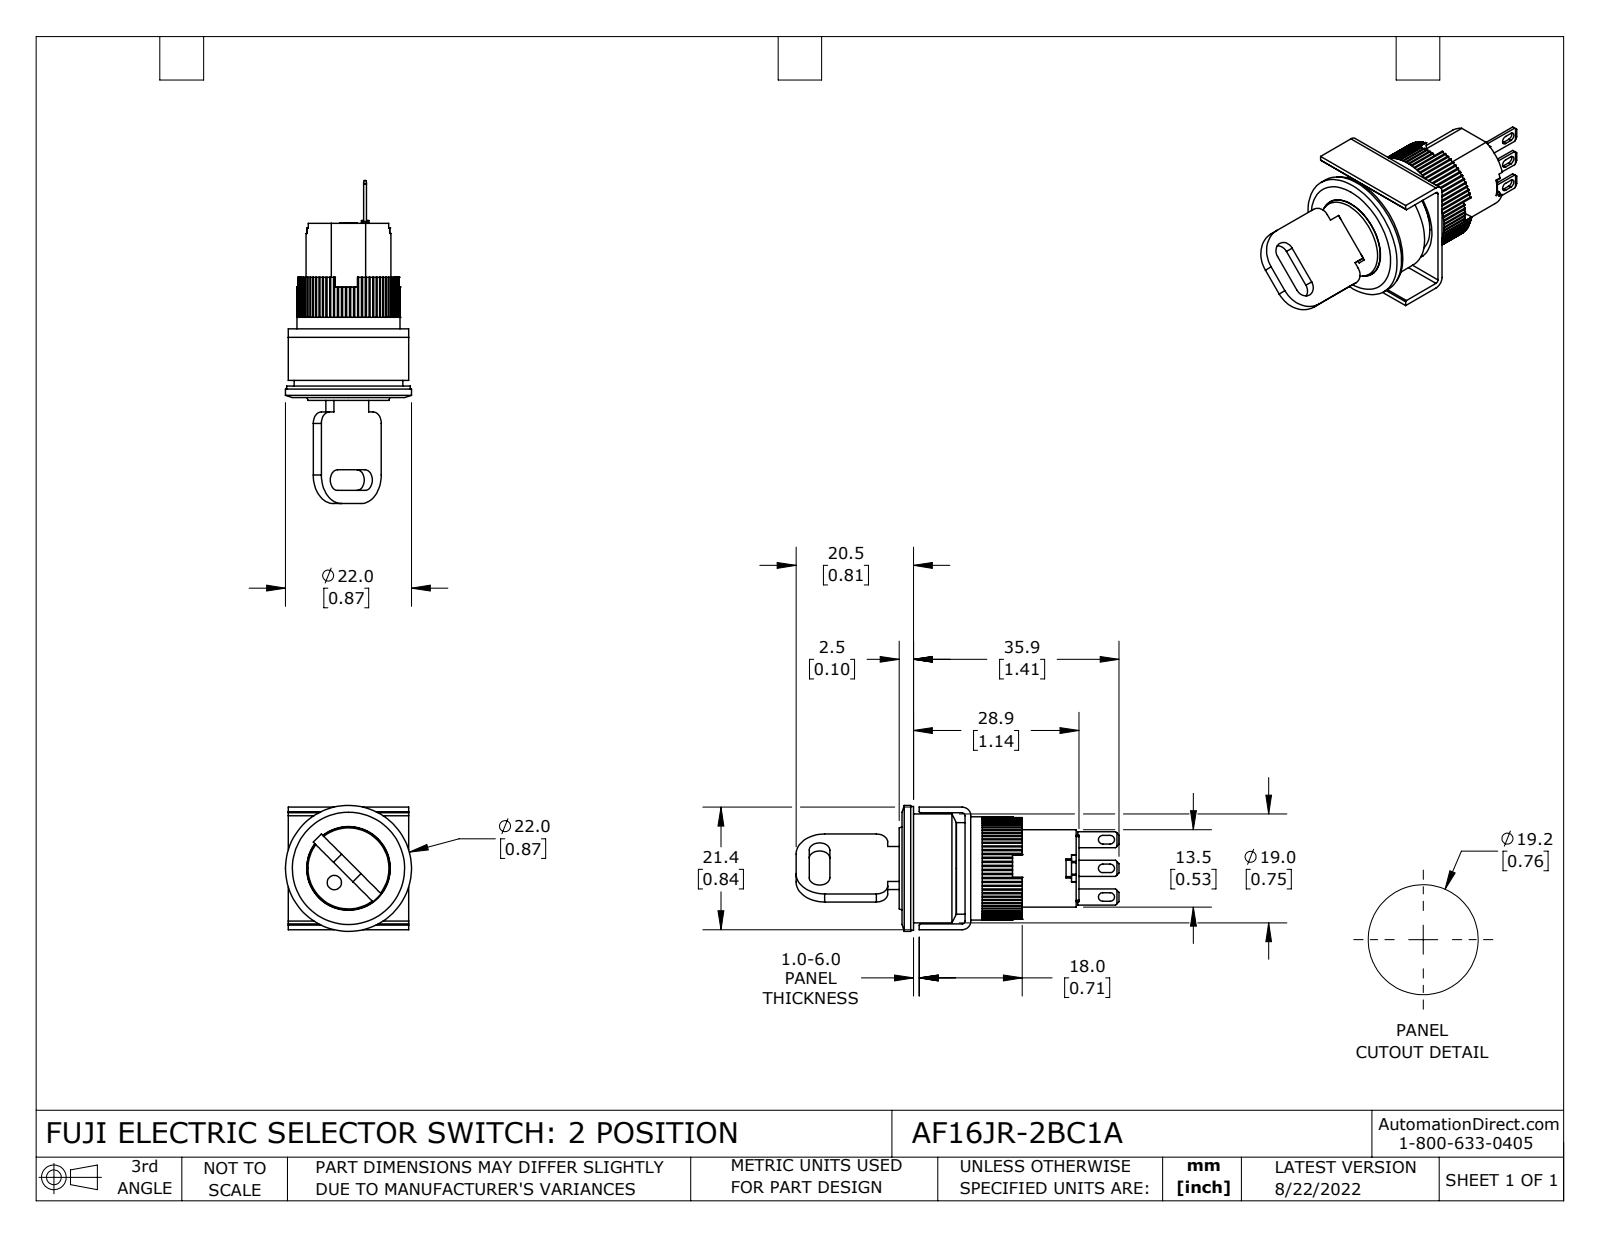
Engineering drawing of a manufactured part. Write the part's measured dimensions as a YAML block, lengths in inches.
part_name: "AF16JR-2BC1A"
step_written_by: "SolidWorks 2021 (CONFIG_CONTROL_DESIGN)"
units: inches
bodies: {solids: 10, faces: 639, planar: 456, cylindrical: 177, other: 6}
overall_size: [2.22, 0.866, 0.866]
volume: 0.493
surface_area: 11.01
round_holes:
  - {diameter: 0.039, count: 1}
  - {diameter: 0.098, count: 1}
  - {diameter: 0.575, count: 1}
  - {diameter: 0.709, count: 1}
  - {diameter: 0.748, count: 1}
round_bosses_or_shafts:
  - {diameter: 0.866, count: 1}
  - {diameter: 0.85, count: 1}
  - {diameter: 0.63, count: 1}
  - {diameter: 0.583, count: 1}
  - {diameter: 0.571, count: 1}
partial_cylinders:
  - {radius: 0.01, count: 80}
  - {radius: 0.008, count: 12}
  - {radius: 0.03, count: 6}
  - {radius: 0.02, count: 2}
  - {radius: 0.059, count: 2}
  - {radius: 0.071, count: 2}
  - {radius: 0.079, count: 2}
  - {radius: 0.197, count: 2}
face_to_face_distances: [0.079, 0.039, 0.02, 0.374, 0.177, 0.394, 0.803, 0.098, 0.059, 0.764]
hole_center_spacings: [0.137]
